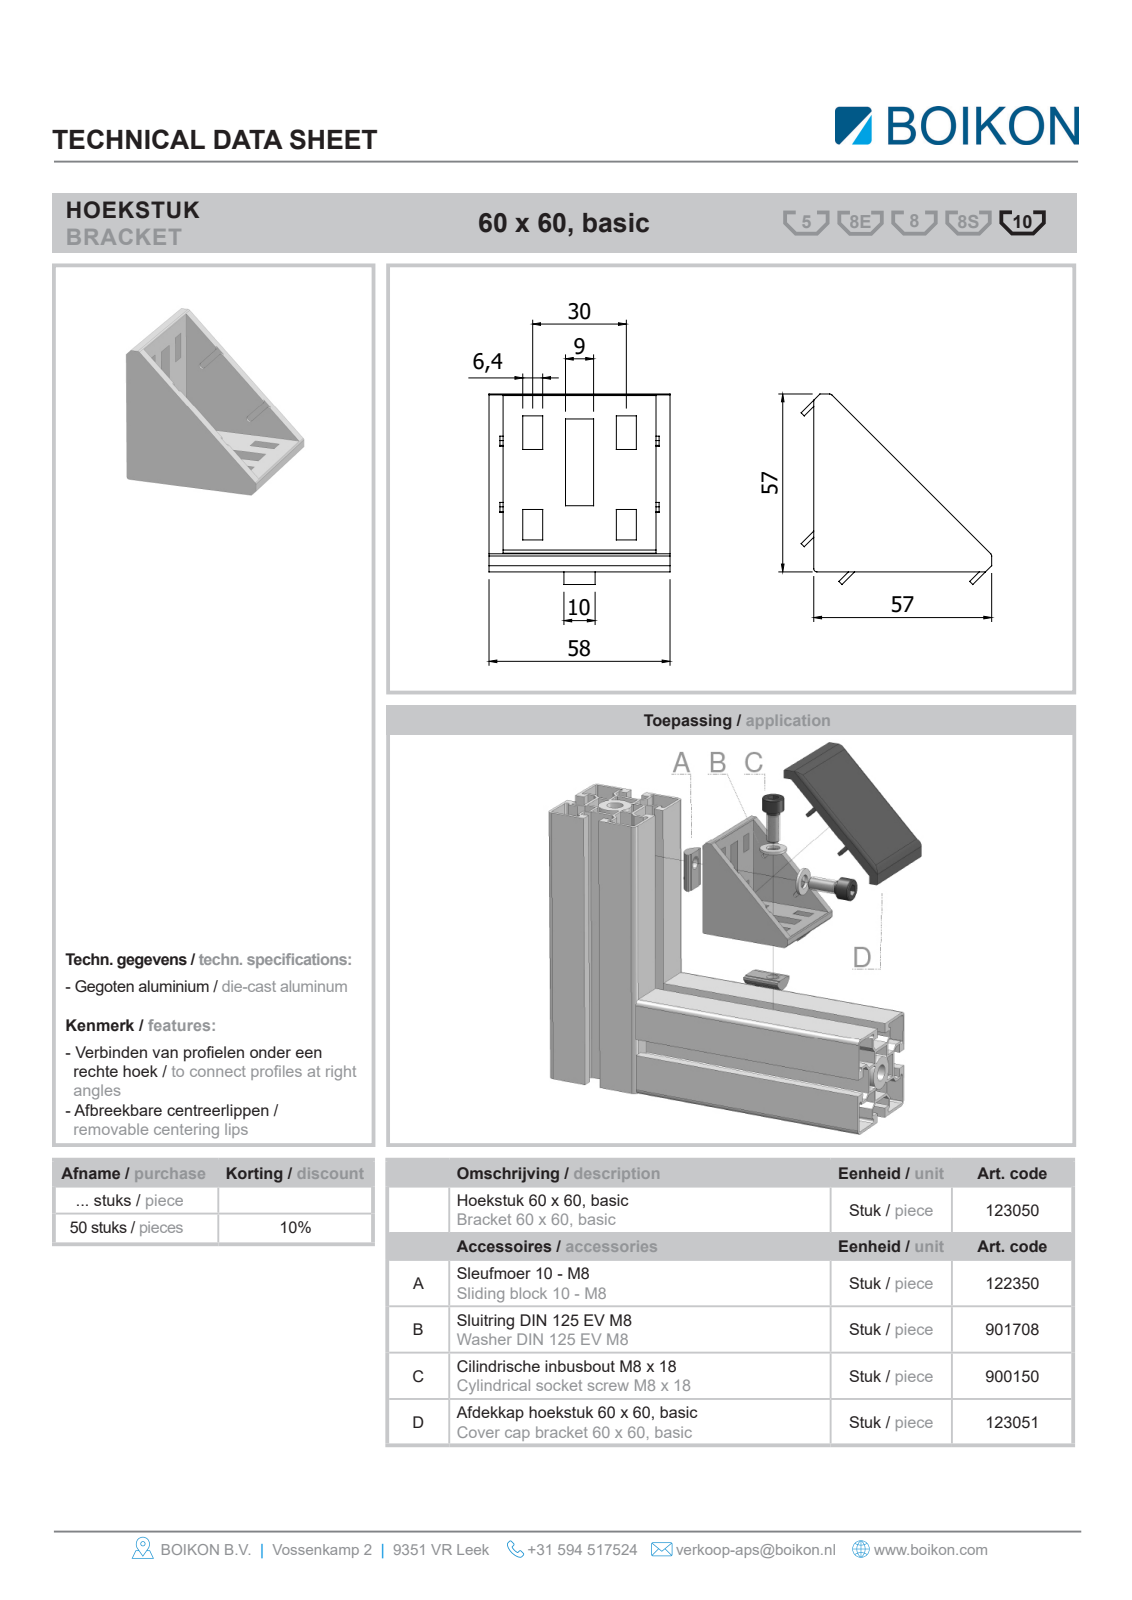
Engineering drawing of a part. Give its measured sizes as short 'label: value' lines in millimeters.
name: Root; 123050HOEKSTUK 60X60BOIKON; 123051AFDEKKAP 60X60 BASICBOIKON; 900152Cil. inbusbout DIN 912 EV M8 x 20BOIKON0 (+2 more)
written by: HiCAD 2013 1802.4 Build 509 (AUTOMOTIVE_DESIGN)
unit: mm
bodies: 8 solids, 243 faces (190 planar, 41 cylindrical, 12 other)
size: 71.93 × 71.93 × 58
volume: 59 819 mm³; area: 35 989 mm²
holes: 2× ⌀8, 2× ⌀8.4
bosses: 2× ⌀16, 2× ⌀13, 2× ⌀6.47
rounds: 8× R1, 8× R1.5, 2× R1.3, 2× R8
face distances: 6, 3, 4.5, 53.5, 58, 49, 20, 30, 29, 33.5
